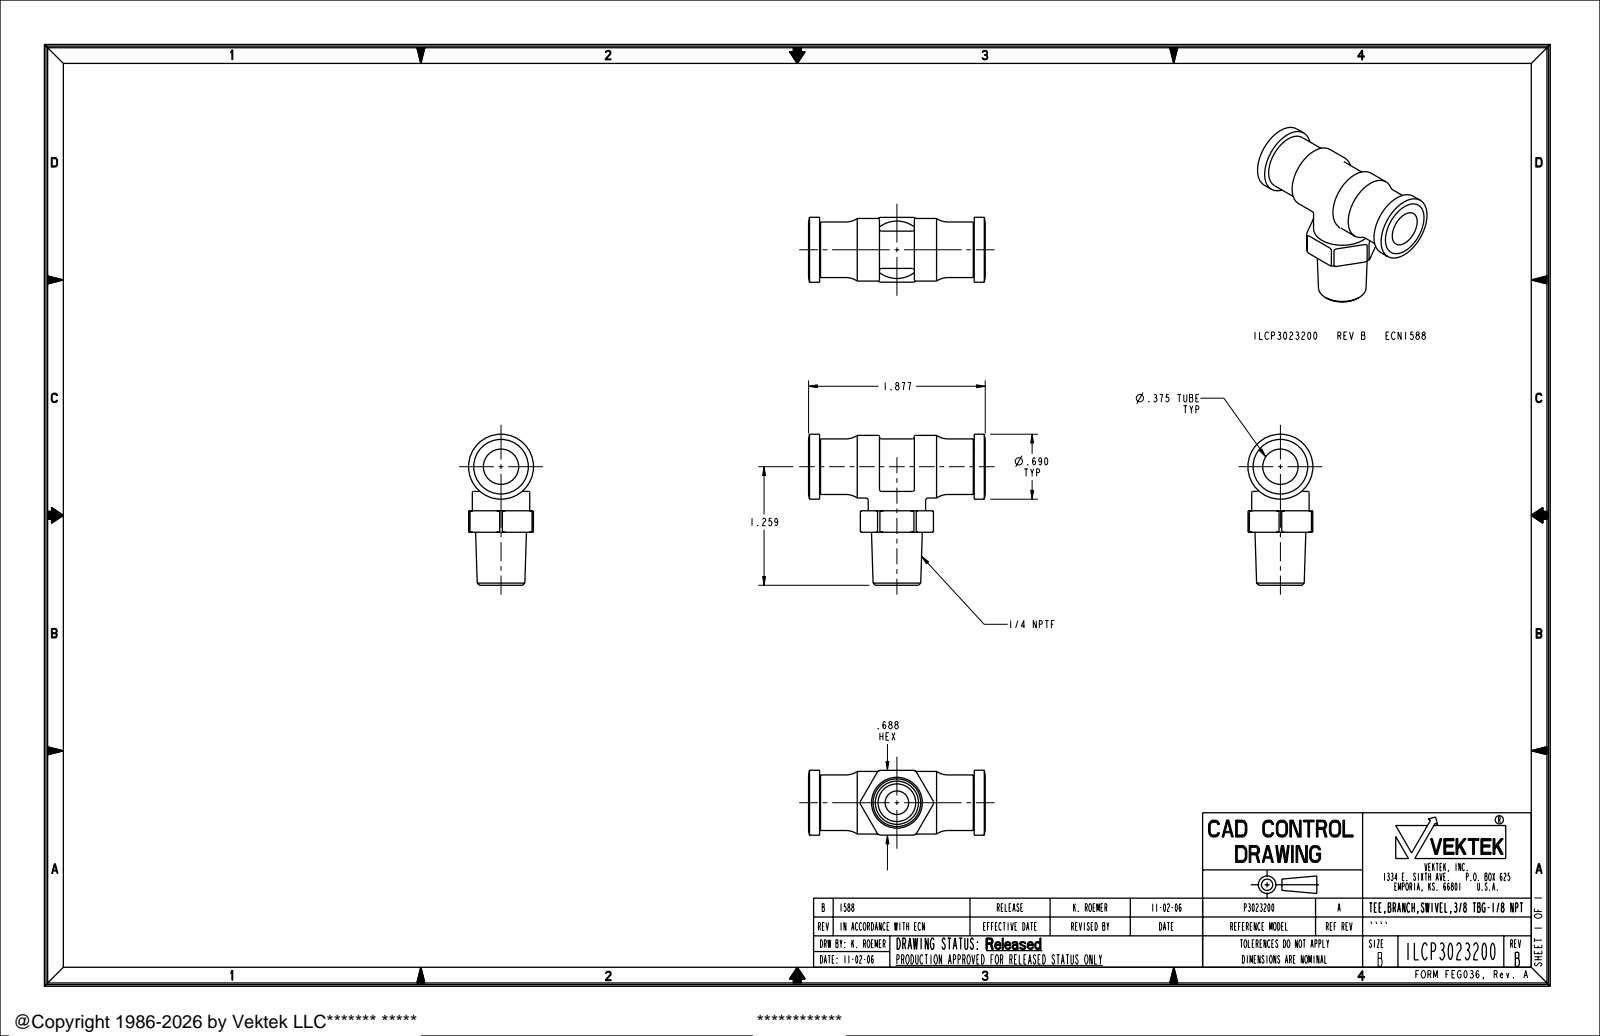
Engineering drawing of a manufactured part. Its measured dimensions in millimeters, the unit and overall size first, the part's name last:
Units: millimetres
Overall size (bounding box): 47.7 × 40.7 × 17.5
Round holes (diameter × count): ⌀6.4 ×1, ⌀9.5 ×1, ⌀10.2 ×1
Round bosses / shafts (diameter × count): ⌀17.5 ×1, ⌀16.9 ×1, ⌀15.5 ×1, ⌀15 ×1, ⌀9.9 ×1
Partial cylindrical surfaces — rounded edges, fillets, slot ends (radius × count): R0.5 ×10, R9.9 ×1
Main face-to-face distances: 41.5, 3, 3.2, 44.5, 44.7, 41.7, 17.4, 3.7, 13.8, 41.2
Volume: 8 230 mm³ · Surface area: 6 839 mm²
Bodies: 1 solid, 119 faces (22 planar, 43 cylindrical, 54 other)
Part name (STEP PRODUCT): ILCP3023200
STEP written by: PRO/ENGINEER BY PARAMETRIC TECHNOLOGY CORPORATION, 2005180 (AUTOMOTIVE_DESIGN_CC2)
